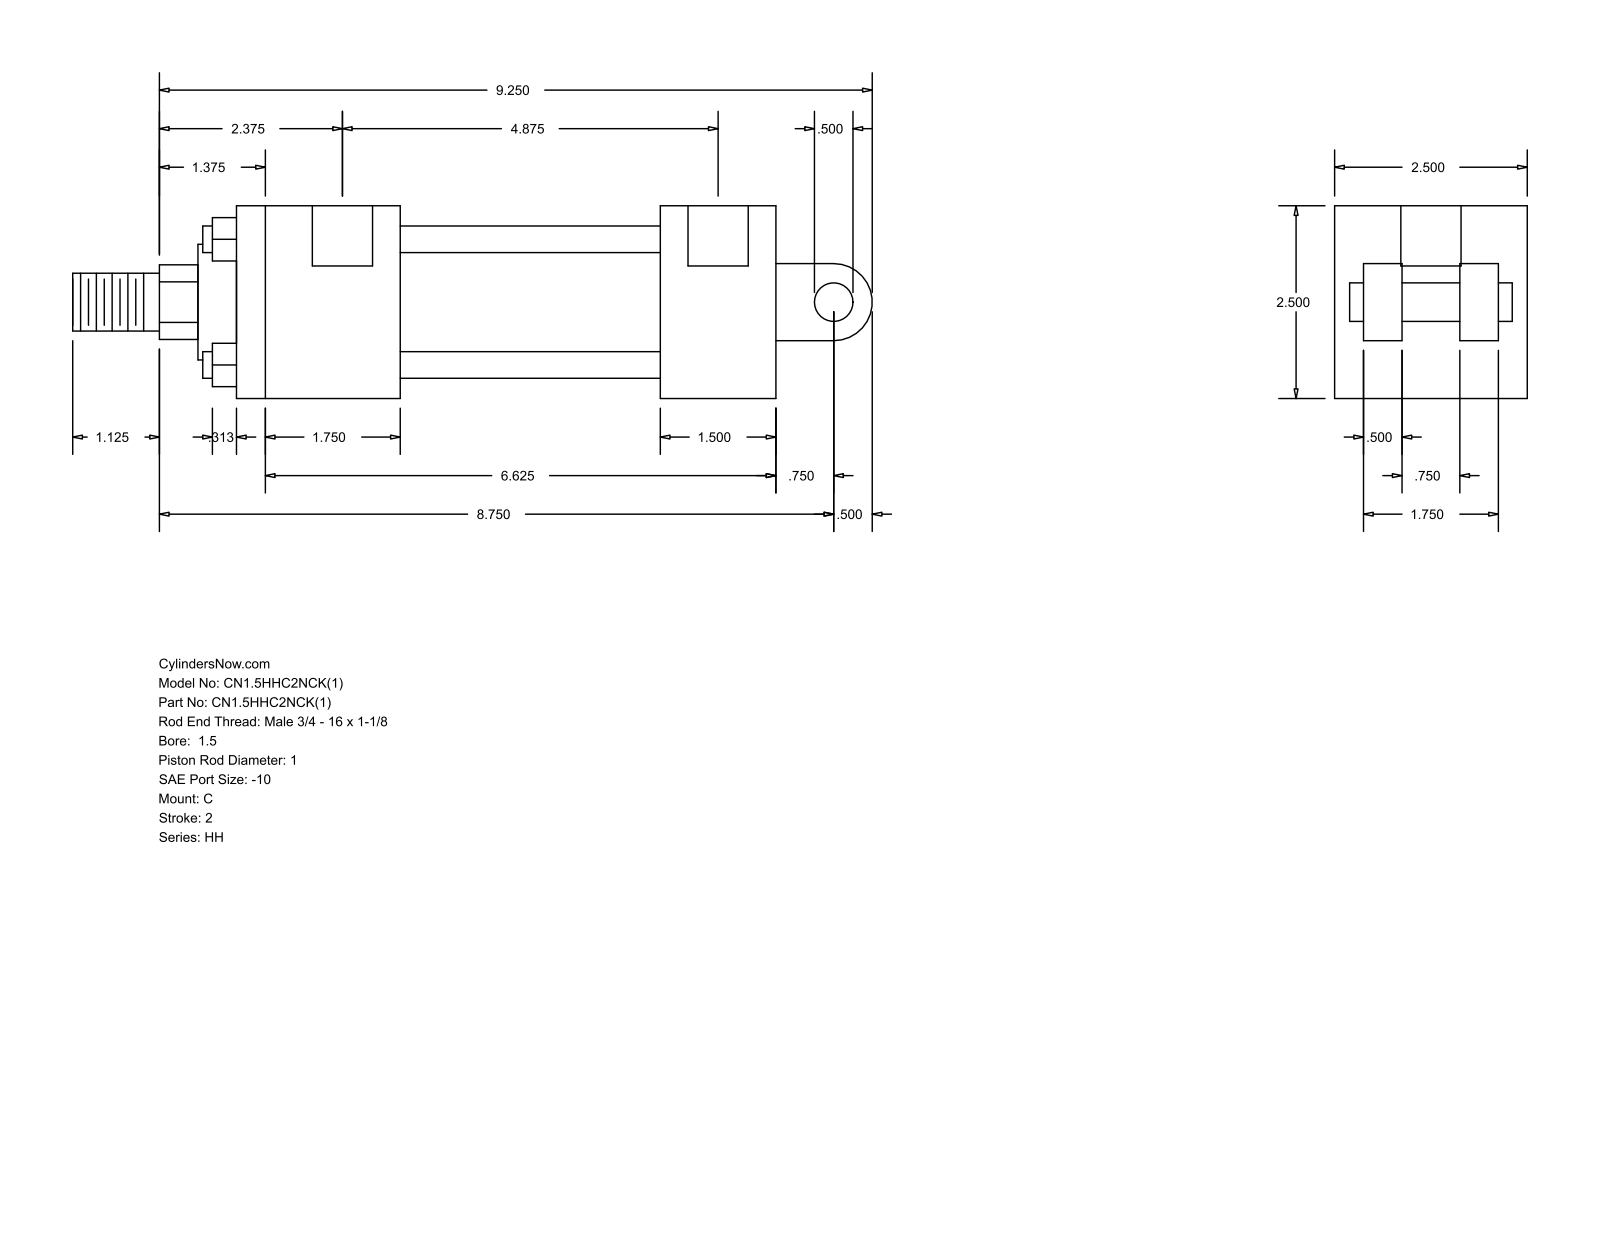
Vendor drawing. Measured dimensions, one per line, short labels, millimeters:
name: HH_C__0150_1
written by: GSSL Pune (CONFIG_CONTROL_DESIGN)
unit: mm
bodies: 0 solids, 99 faces (70 planar, 29 cylindrical, 0 other)
size: 263.52 × 63.5 × 63.5
holes: 4× ⌀5.56, 2× ⌀19.84
bosses: 4× ⌀8.76, 1× ⌀44.45, 1× ⌀38.1, 1× ⌀25.4, 1× ⌀19.05, 1× ⌀12.7
rounds: 1× R12.29, 1× R12.7
face distances: 63.5, 53.98, 38.1, 85.72, 123.82, 139.7, 177.8, 12.7, 22.22, 41.28
hole spacings: 1.59, 125.41, 127, 123.82
